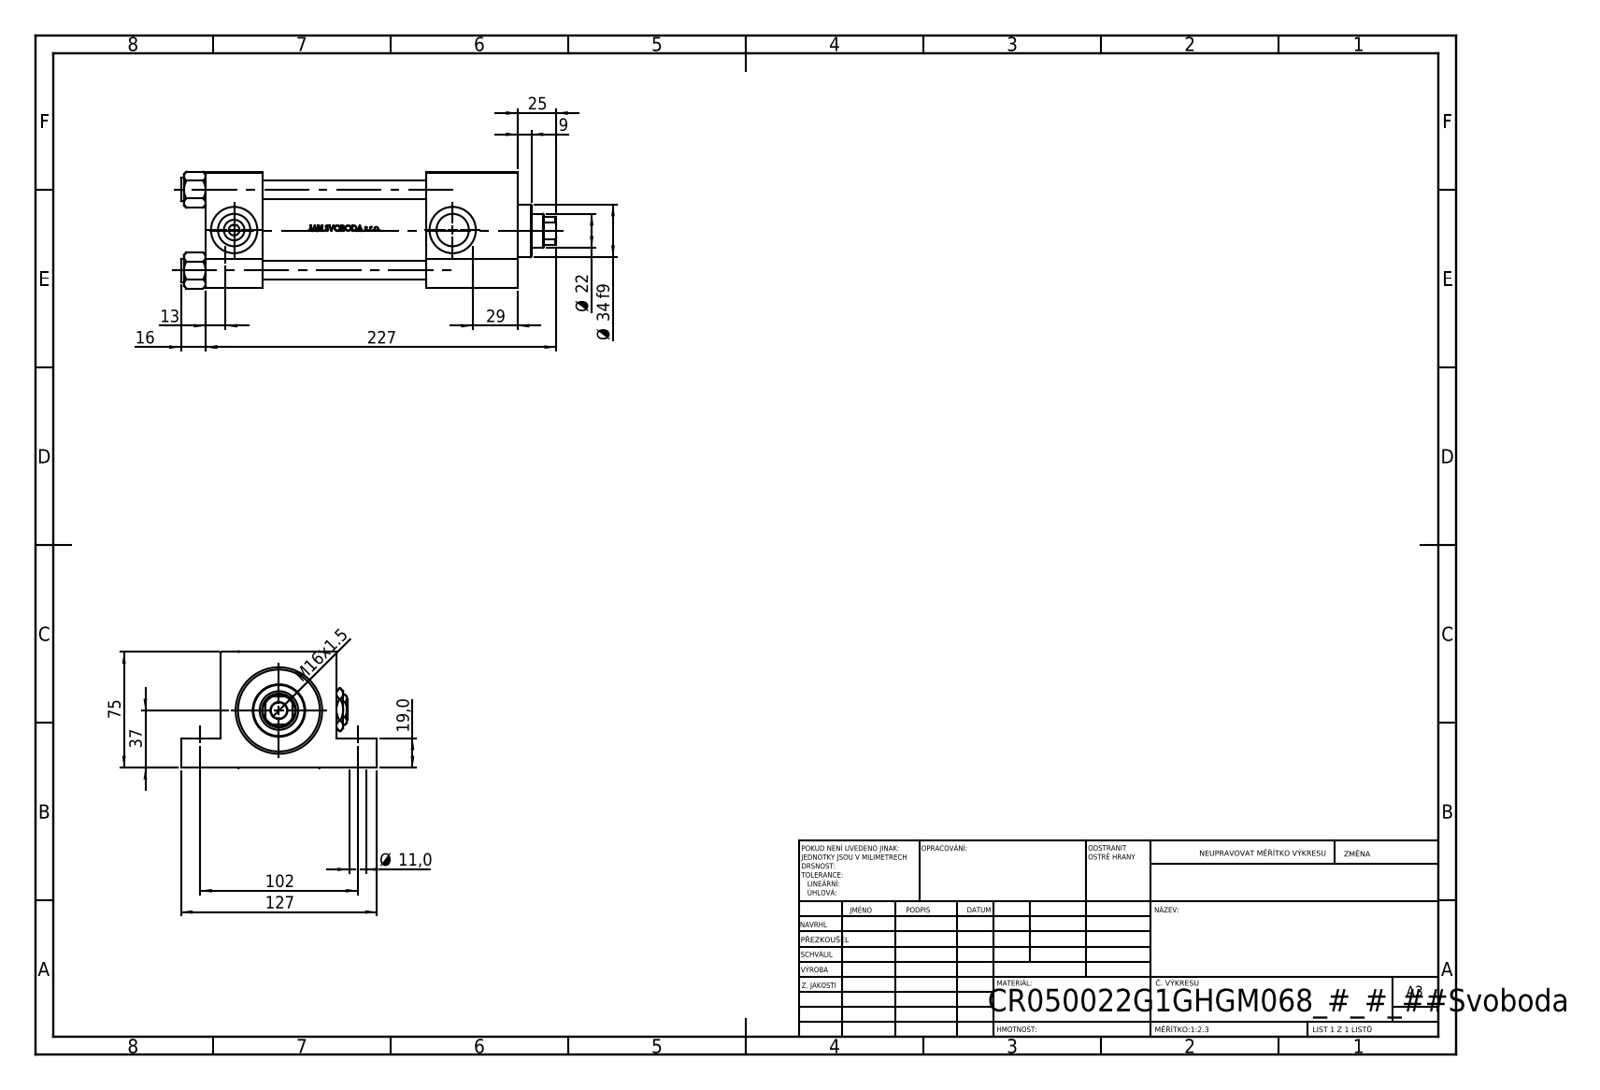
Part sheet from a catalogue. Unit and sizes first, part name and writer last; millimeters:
Units: millimetres
Overall size (bounding box): 243 × 127 × 75.54
Round holes (diameter × count): ⌀11 ×4, ⌀12 ×4, ⌀7 ×2, ⌀20.96 ×2, ⌀30 ×2, ⌀10.5 ×1, ⌀22 ×1, ⌀25 ×1, ⌀41 ×1, ⌀50 ×1, ⌀53 ×1
Round bosses / shafts (diameter × count): ⌀15 ×4, ⌀56 ×1, ⌀34 ×1
Partial cylindrical surfaces — rounded edges, fillets, slot ends (radius × count): R10.5 ×1
Main face-to-face distances: 75, 37, 202, 165, 19, 56, 143, 106, 59, 26
Hole centre spacings: 52.3, 36.63, 37.34, 73.96, 102, 160, 189.75, 141.5
Volume: 816 341 mm³ · Surface area: 187 844 mm²
Bodies: 12 solids, 1134 faces (454 planar, 128 cylindrical, 552 other)
Part name (STEP PRODUCT): V215CR_VCP_G; V215CR_G_Body; V215CR_G_TYCINKA; V215_VC_A (+2 more)
STEP written by: SolidWorks 2019 (CONFIG_CONTROL_DESIGN)
